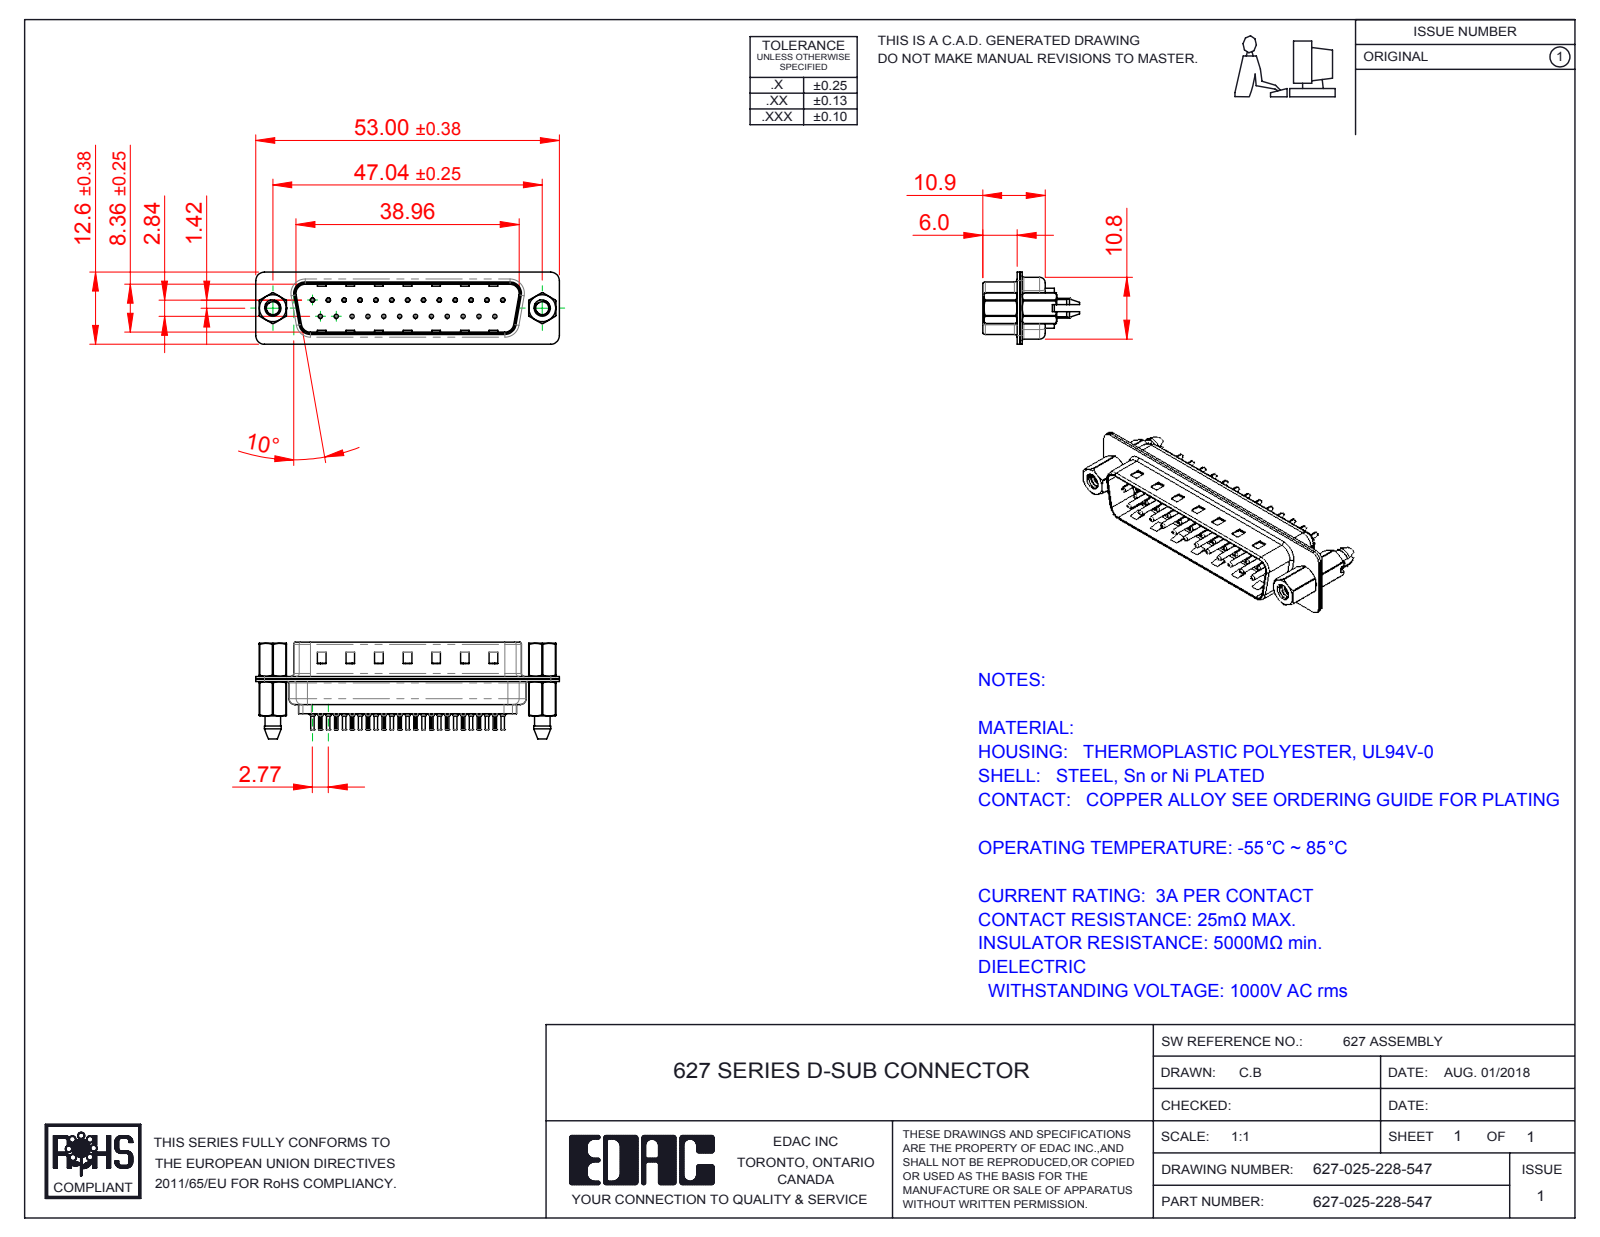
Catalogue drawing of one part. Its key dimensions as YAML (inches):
part_name: "627 Contact Row 1_28L; 627 4-40 Threaded Boardlock_LP; 627-025-228-547; 627 Housing_25 LP (+4 more)"
step_written_by: "SolidWorks 2016 (CONFIG_CONTROL_DESIGN)"
units: inches
bodies: {solids: 32, faces: 3026, planar: 825, cylindrical: 1166, other: 1035}
overall_size: [2.087, 0.665, 0.496]
volume: 0.183
surface_area: 13.07
round_holes:
  - {diameter: 0.008, count: 25}
  - {diameter: 0.014, count: 25}
  - {diameter: 0.043, count: 25}
  - {diameter: 0.063, count: 25}
  - {diameter: 0.089, count: 2}
  - {diameter: 0.09, count: 2}
  - {diameter: 0.157, count: 2}
  - {diameter: 0.189, count: 2}
round_bosses_or_shafts:
  - {diameter: 0.079, count: 25}
  - {diameter: 0.059, count: 25}
  - {diameter: 0.03, count: 25}
  - {diameter: 0.024, count: 25}
  - {diameter: 0.193, count: 2}
  - {diameter: 0.11, count: 2}
partial_cylinders:
  - {radius: 0.004, count: 50}
  - {radius: 0.059, count: 18}
  - {radius: 0.079, count: 12}
  - {radius: 0.063, count: 10}
  - {radius: 0.02, count: 8}
  - {radius: 0.01, count: 4}
  - {radius: 0.024, count: 4}
  - {radius: 0.026, count: 4}
face_to_face_distances: [0.016, 0.018, 0.032, 0.377, 0.345, 0.035, 0.059, 0.055, 0.256, 0.238]
hole_center_spacings: [0.124, 0.327, 0.109, 0.218, 0.436, 0.654, 0.198, 0.198]
